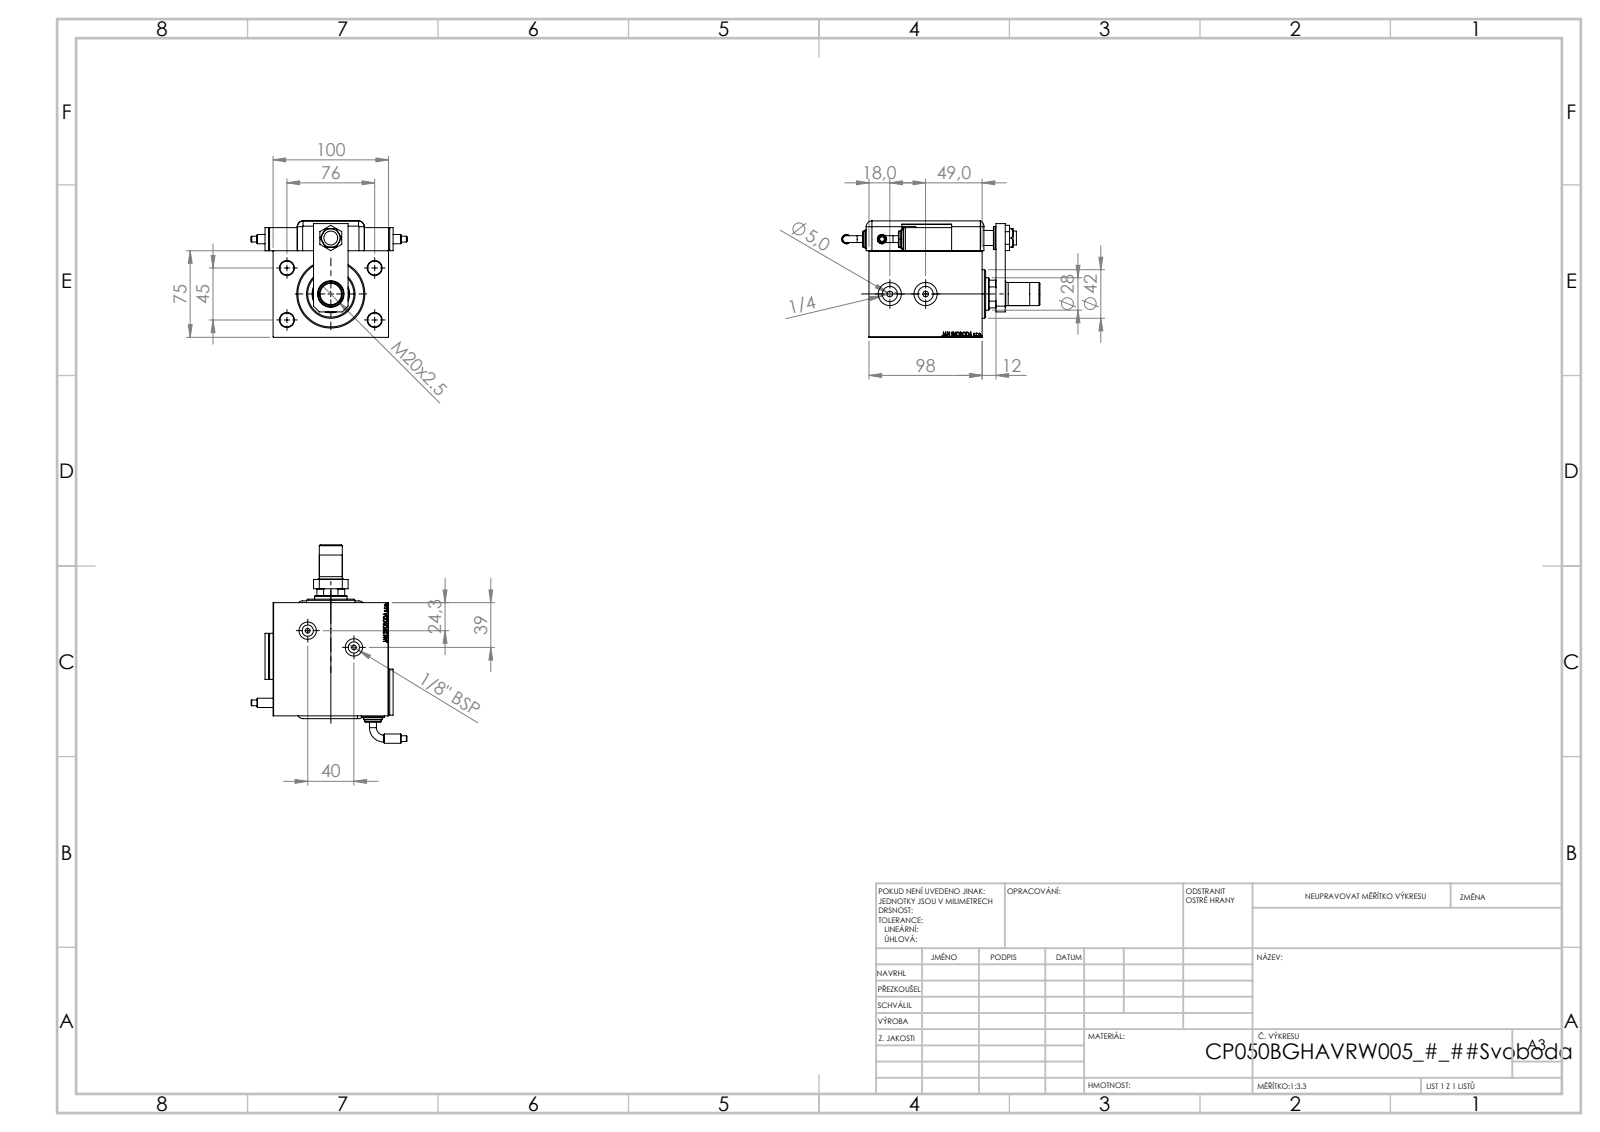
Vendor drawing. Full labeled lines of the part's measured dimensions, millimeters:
Part name (STEP PRODUCT): SWITCH DIM A_G; V450CM_MALE_METRIC; V450CP_VC_B; NUT_D19 (+7 more)
STEP written by: SolidWorks 2019 (CONFIG_CONTROL_DESIGN)
Units: millimetres
Bodies: 15 solids, 1344 faces (624 planar, 139 cylindrical, 581 other)
Overall size (bounding box): 171.76 × 135.01 × 100.8
Volume: 867 029 mm³ · Surface area: 164 307 mm²
Round holes (diameter × count): ⌀12 ×5, ⌀4 ×4, ⌀5 ×2, ⌀8 ×2, ⌀9.73 ×2, ⌀13.16 ×2, ⌀15 ×2, ⌀20 ×2, ⌀13 ×1, ⌀14 ×1, ⌀18.5 ×1, ⌀28 ×1
Round bosses / shafts (diameter × count): ⌀20 ×4, ⌀16 ×2, ⌀14 ×2, ⌀8 ×2, ⌀6 ×2, ⌀5.04 ×2, ⌀42 ×1, ⌀18 ×1
Partial cylindrical surfaces — rounded edges, fillets, slot ends (radius × count): R5 ×9, R10 ×1, R13.5 ×1
Main face-to-face distances: 3, 75, 98, 100, 20, 14, 49, 84, 25.8, 100.8
Hole centre spacings: 44.16, 45, 46.04, 76, 80.53, 88.32, 18.28, 20
